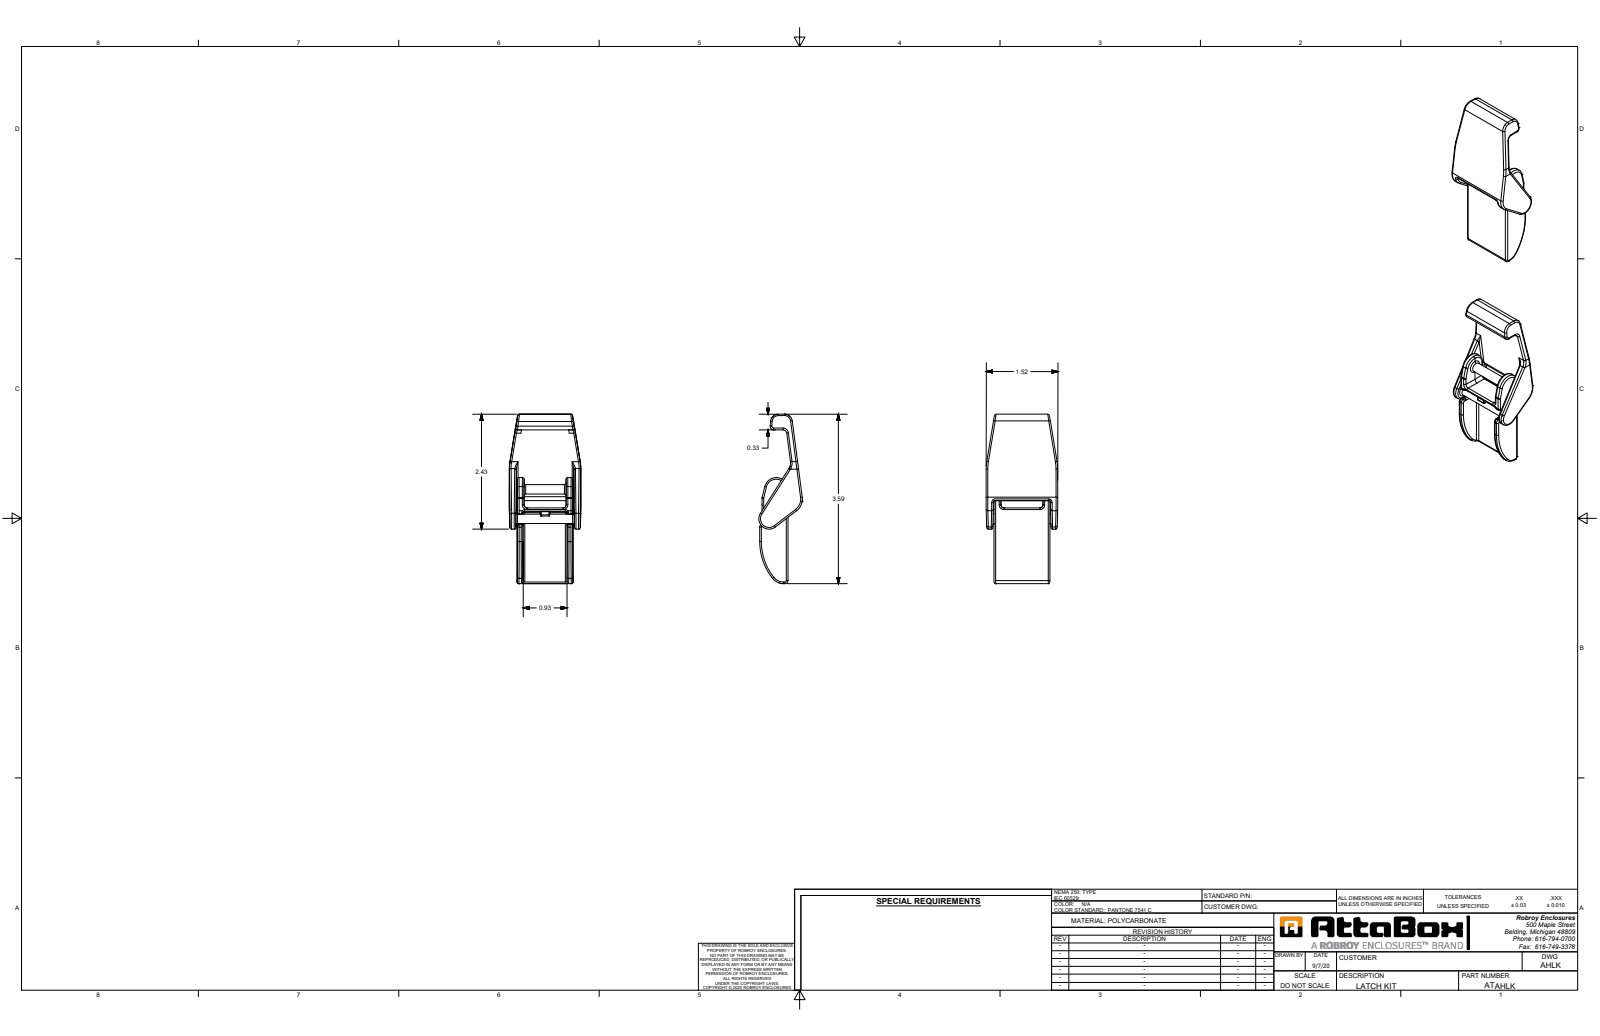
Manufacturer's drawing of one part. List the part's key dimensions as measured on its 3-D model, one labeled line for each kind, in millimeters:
Part name (STEP PRODUCT): AHLK
STEP written by: SolidWorks 2019 (AUTOMOTIVE_DESIGN)
Units: millimetres
Bodies: 2 solids, 268 faces (51 planar, 115 cylindrical, 102 other)
Overall size (bounding box): 91.3 × 38.6 × 23.4
Volume: 20 090 mm³ · Surface area: 12 680 mm²
Round bosses / shafts (diameter × count): ⌀5.1 ×2
Partial cylindrical surfaces — rounded edges, fillets, slot ends (radius × count): R0.9 ×63, R0.3 ×12, R1.7 ×9, R0.6 ×3, R2.4 ×2, R4.2 ×2, R1.9 ×1, R2 ×1
Main face-to-face distances: 3.8, 3.8, 34.7, 26.8, 4.1, 4.1, 30.6, 30.6, 30.9, 3.8
